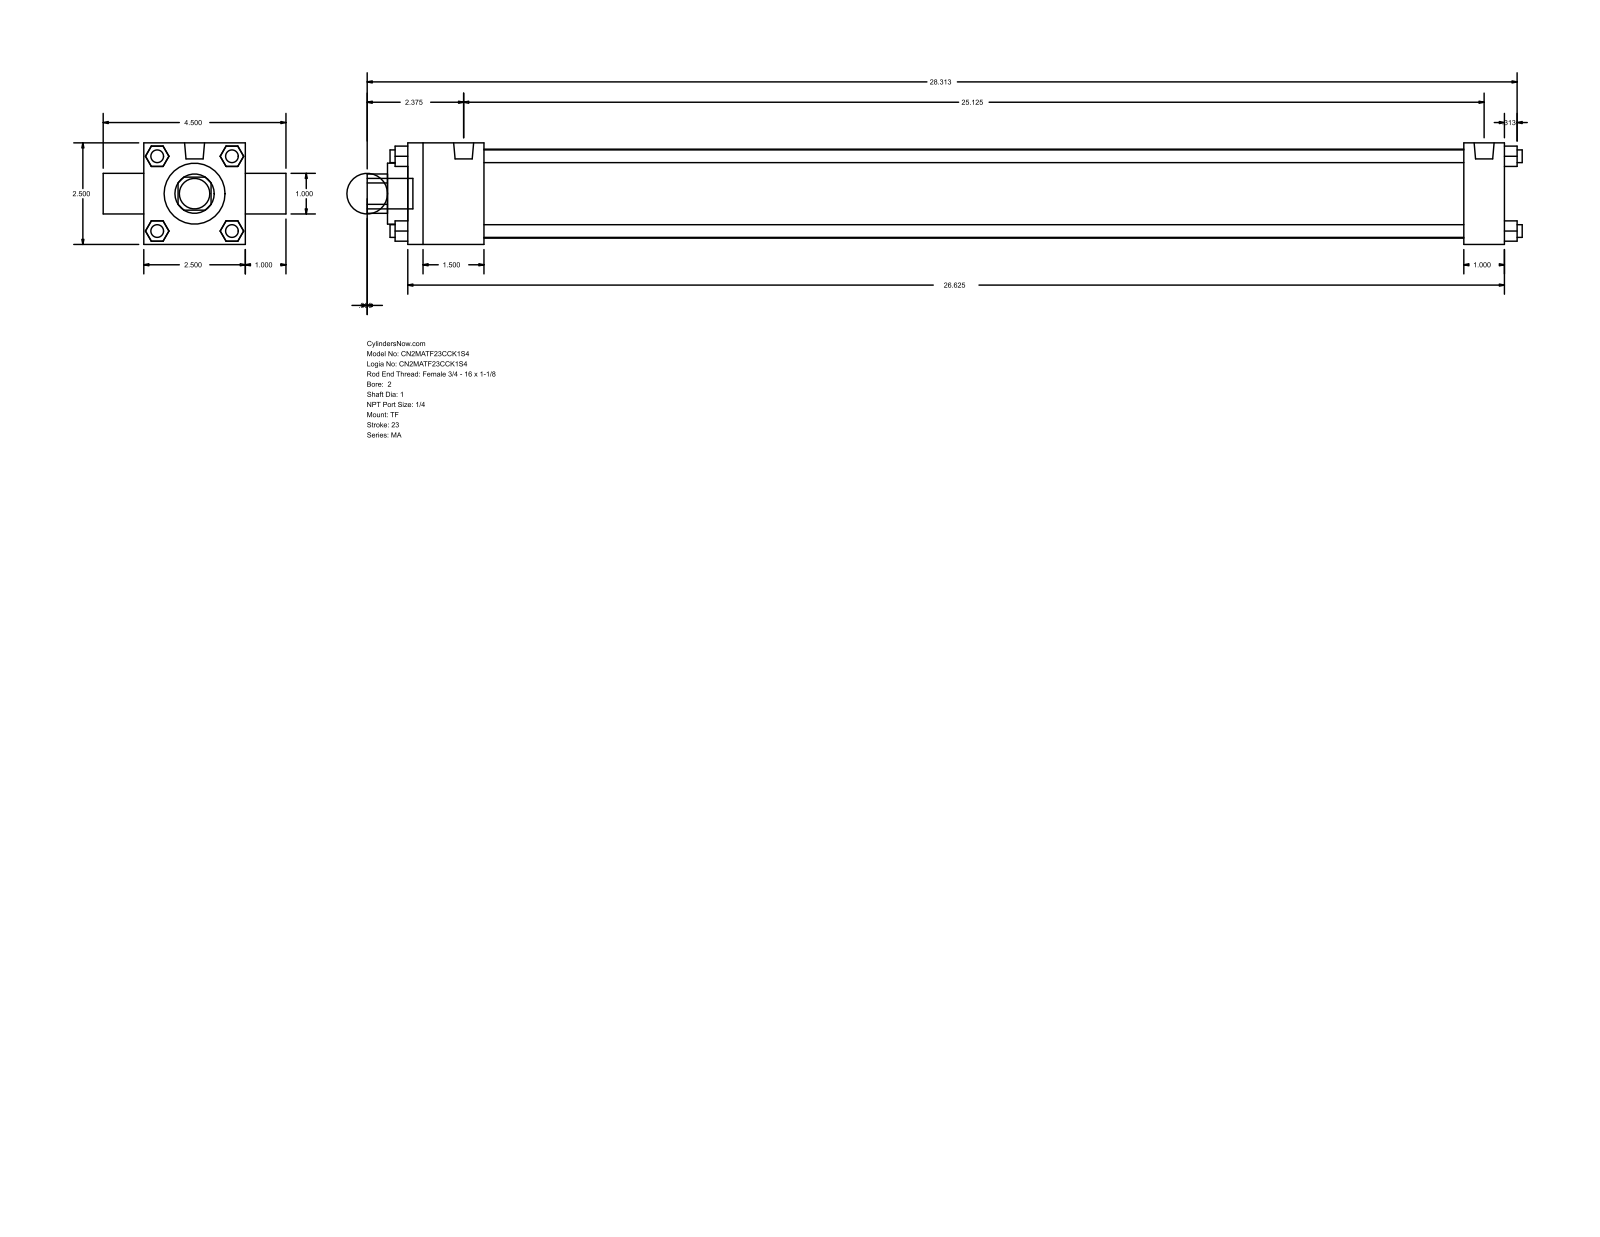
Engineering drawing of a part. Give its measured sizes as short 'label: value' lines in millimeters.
name: MA_TF__0200_1
written by: GSSL Pune (CONFIG_CONTROL_DESIGN)
unit: mm
bodies: 0 solids, 120 faces (92 planar, 28 cylindrical, 0 other)
size: 722.31 × 114.3 × 63.5
holes: 2× ⌀25.4, 1× ⌀38.1, 1× ⌀55.63
bosses: 7× ⌀7.94, 2× ⌀12.49, 1× ⌀19.05
rounds: 1× R12.29
face distances: 63.5, 25.4, 685.8, 12.7, 47.63, 660.4, 612.77, 638.17, 88.9, 40.47
